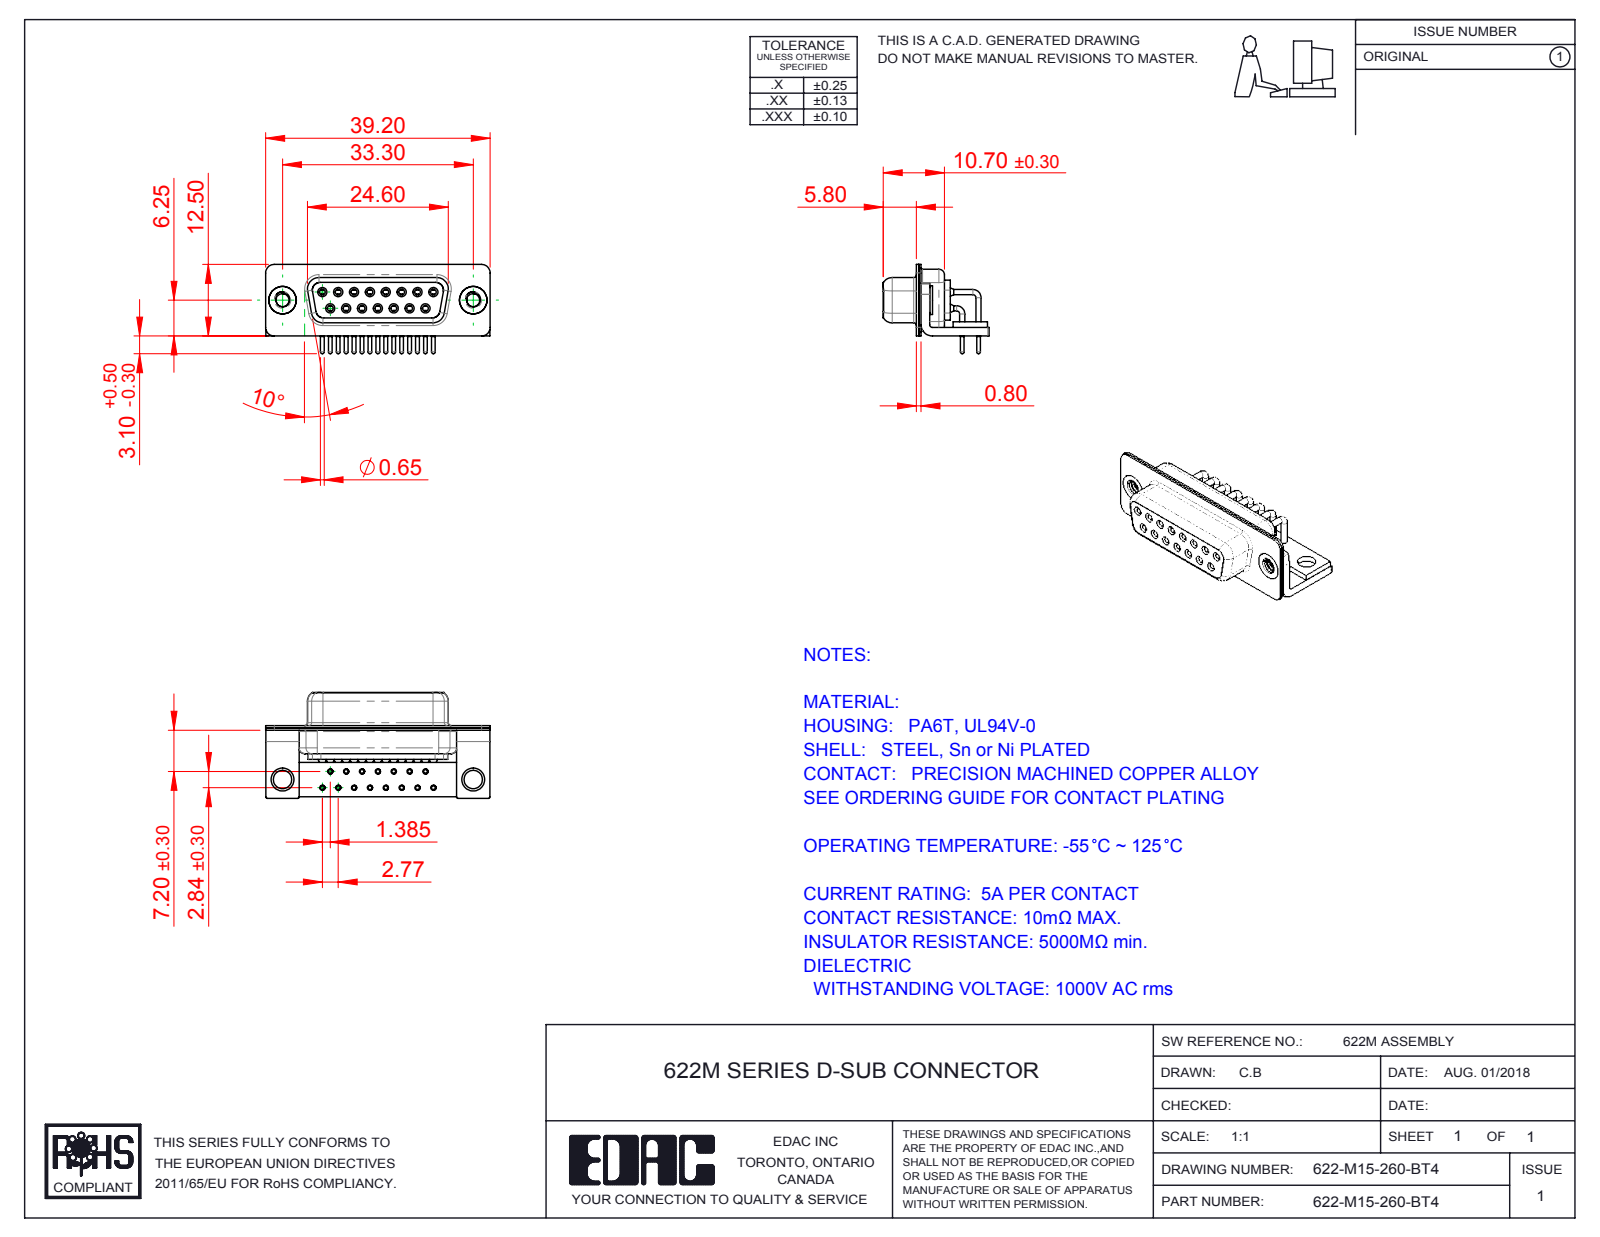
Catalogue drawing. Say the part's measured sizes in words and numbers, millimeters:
The part is named "622-M15-260-BT4; 622M Stabilizer Board_15 Contacts; 622M Stabilizer Bracket; 622M 4-40 Threaded Rivet_Stabilizer (+5 more)". Its 3-D file was written by "SolidWorks 2016 (CONFIG_CONTROL_DESIGN)". It is 23 solids with 1154 faces: 318 planar, 534 cylindrical and 302 other. Overall it measures 39.2 by 18.5 by 15.6 millimeters. Its volume is 2 973 cubic millimeters and its surface area 7 506 square millimeters. Round holes: 15 of diameter 0.9, 15 of diameter 1, 15 of diameter 1.1, 15 of diameter 1.7, 15 of diameter 1.8, 15 of diameter 2, 2 of diameter 2.26, 2 of diameter 3.2, 2 of diameter 4, 2 of diameter 4.8. Round bosses or shafts: 22 of diameter 0.9, 15 of diameter 1.6, 15 of diameter 1.5, 15 of diameter 0.65, 2 of diameter 5, 2 of diameter 4.9. Partial cylindrical surfaces (rounded edges, fillets, slot ends): 16 of radius 0.25, 16 of radius 1.5, 13 of radius 2, 8 of radius 1.35, 8 of radius 1.6, 5 of radius 0.5, 4 of radius 0.6, 4 of radius 0.65. The main face-to-face distances are 0.4, 0.8, 2.3, 1.9, 9.35, 1, 1.5, 1.45, 8.95, 0.85. The hole center spacings are 3.16, 2.77, 5.54, 8.31, 11.08, 5.03, 5.04, 7.48.
